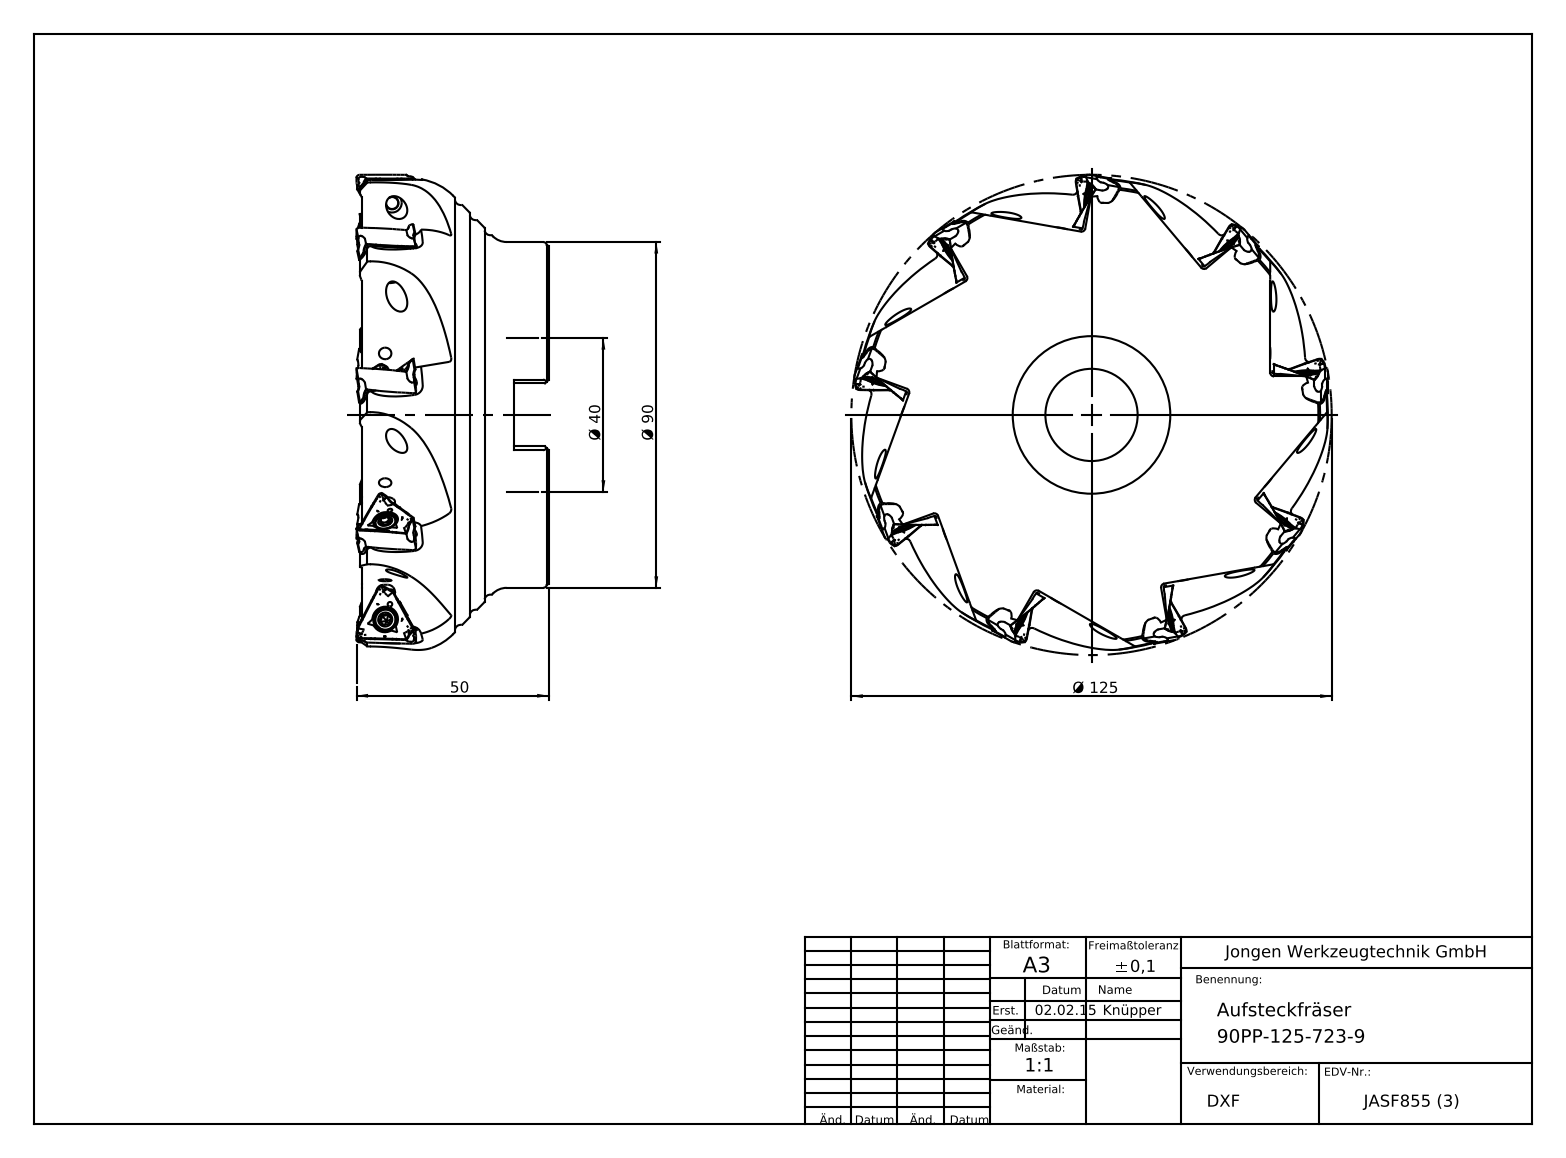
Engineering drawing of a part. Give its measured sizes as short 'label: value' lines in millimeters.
name: 90PP_125_723_9
written by: SolidWorks 2016 (AUTOMOTIVE_DESIGN)
unit: mm
bodies: 1 solid, 587 faces (172 planar, 242 cylindrical, 173 other)
size: 125.83 × 124.92 × 50.01
volume: 388 877 mm³; area: 53 427 mm²
holes: 9× ⌀3, 1× ⌀24, 1× ⌀40, 1× ⌀40.15, 1× ⌀40.3
bosses: 1× ⌀90
rounds: 72× R1.25, 27× R2.5, 18× R2, 9× R0.4, 9× R1, 9× R20
face distances: 48.7, 8.95, 39.75, 28, 19.05, 20.7, 16.4, 1, 62.22, 23.95
